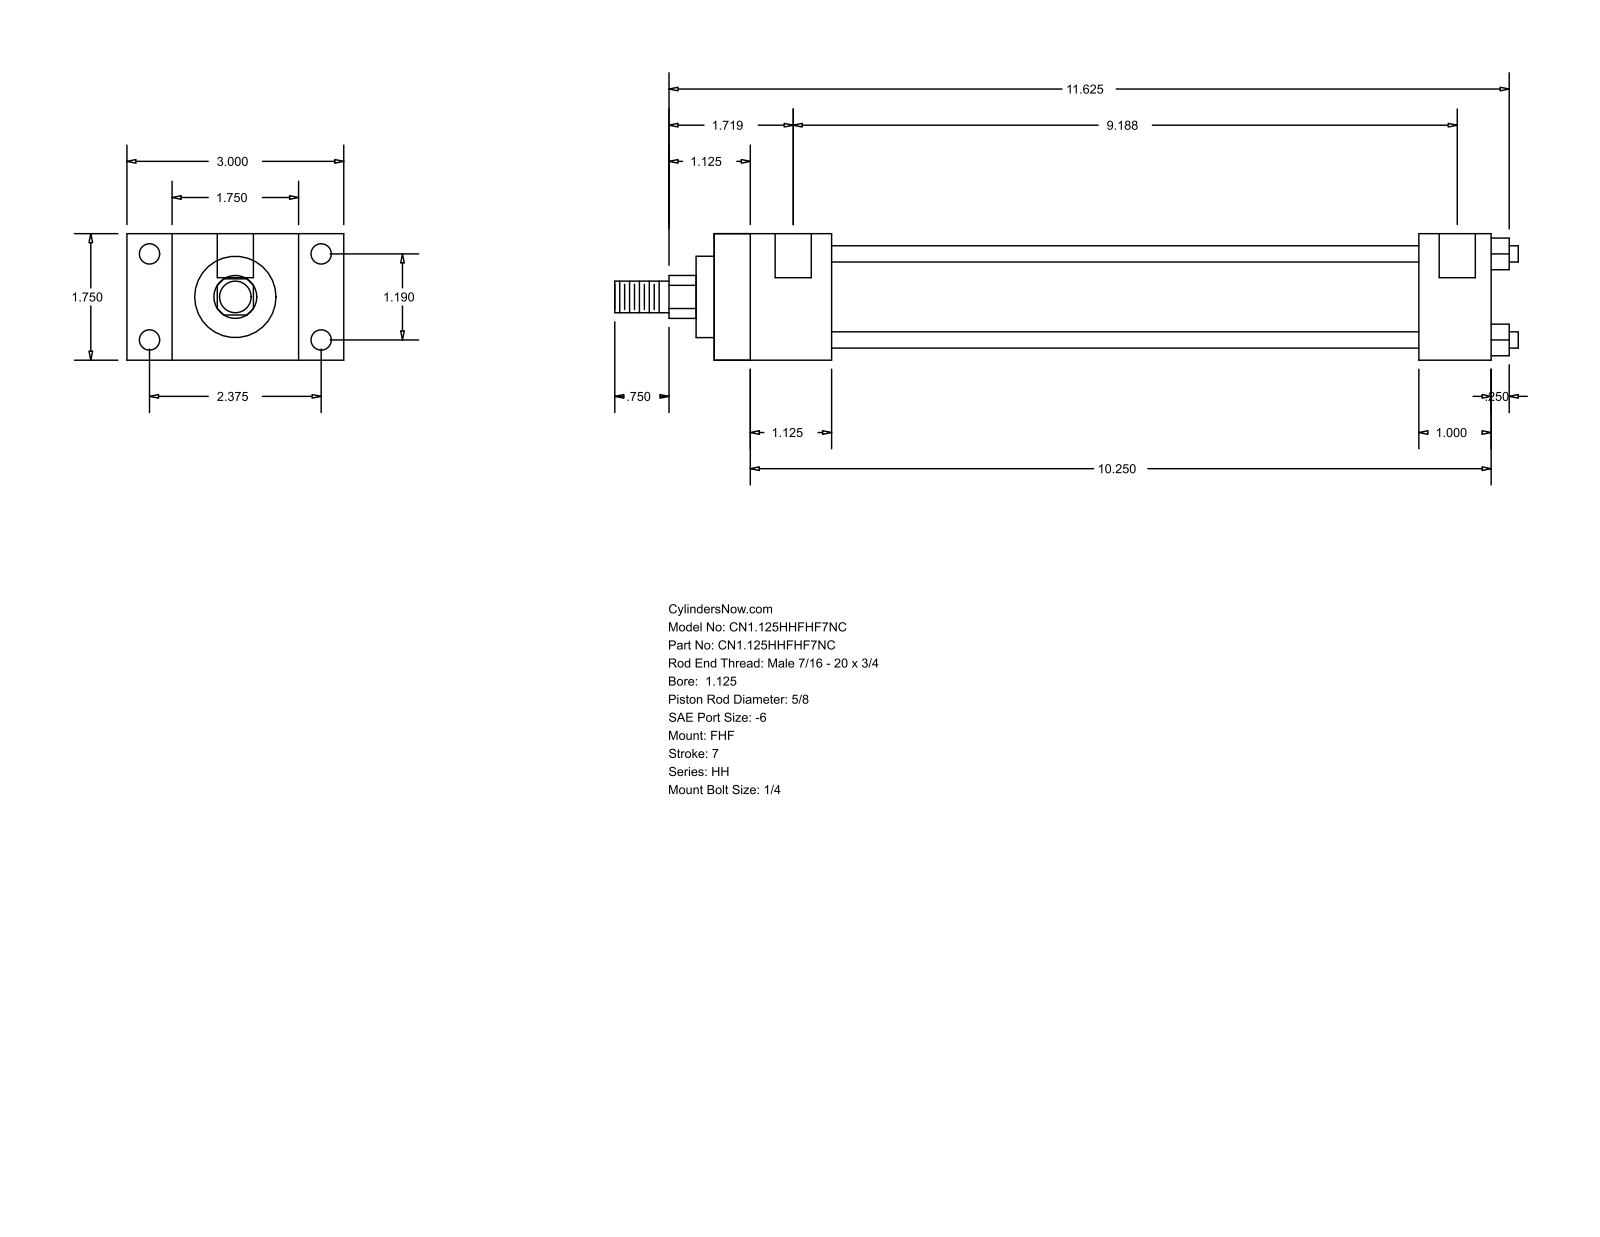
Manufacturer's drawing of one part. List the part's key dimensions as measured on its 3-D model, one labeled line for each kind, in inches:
Part name (STEP PRODUCT): HH_FHF__0112_0.625
STEP written by: GSSL Pune (CONFIG_CONTROL_DESIGN)
Units: inches
Bodies: 0 solids, 88 faces (60 planar, 28 cylindrical, 0 other)
Overall size (bounding box): 12.5 × 3 × 1.75
Round holes (diameter × count): ⌀0.219 ×4, ⌀0.281 ×4, ⌀0.5 ×2
Round bosses / shafts (diameter × count): ⌀0.225 ×4, ⌀1.375 ×1, ⌀1.125 ×1, ⌀0.625 ×1, ⌀0.437 ×1
Partial cylindrical surfaces — rounded edges, fillets, slot ends (radius × count): R0.297 ×1
Main face-to-face distances: 1.75, 0.625, 2.375, 1.625, 3, 10.75, 9.125, 9.75, 8.125, 1
Hole centre spacings: 1.19, 2.375, 2.656, 9.063, 0.125, 9.187
